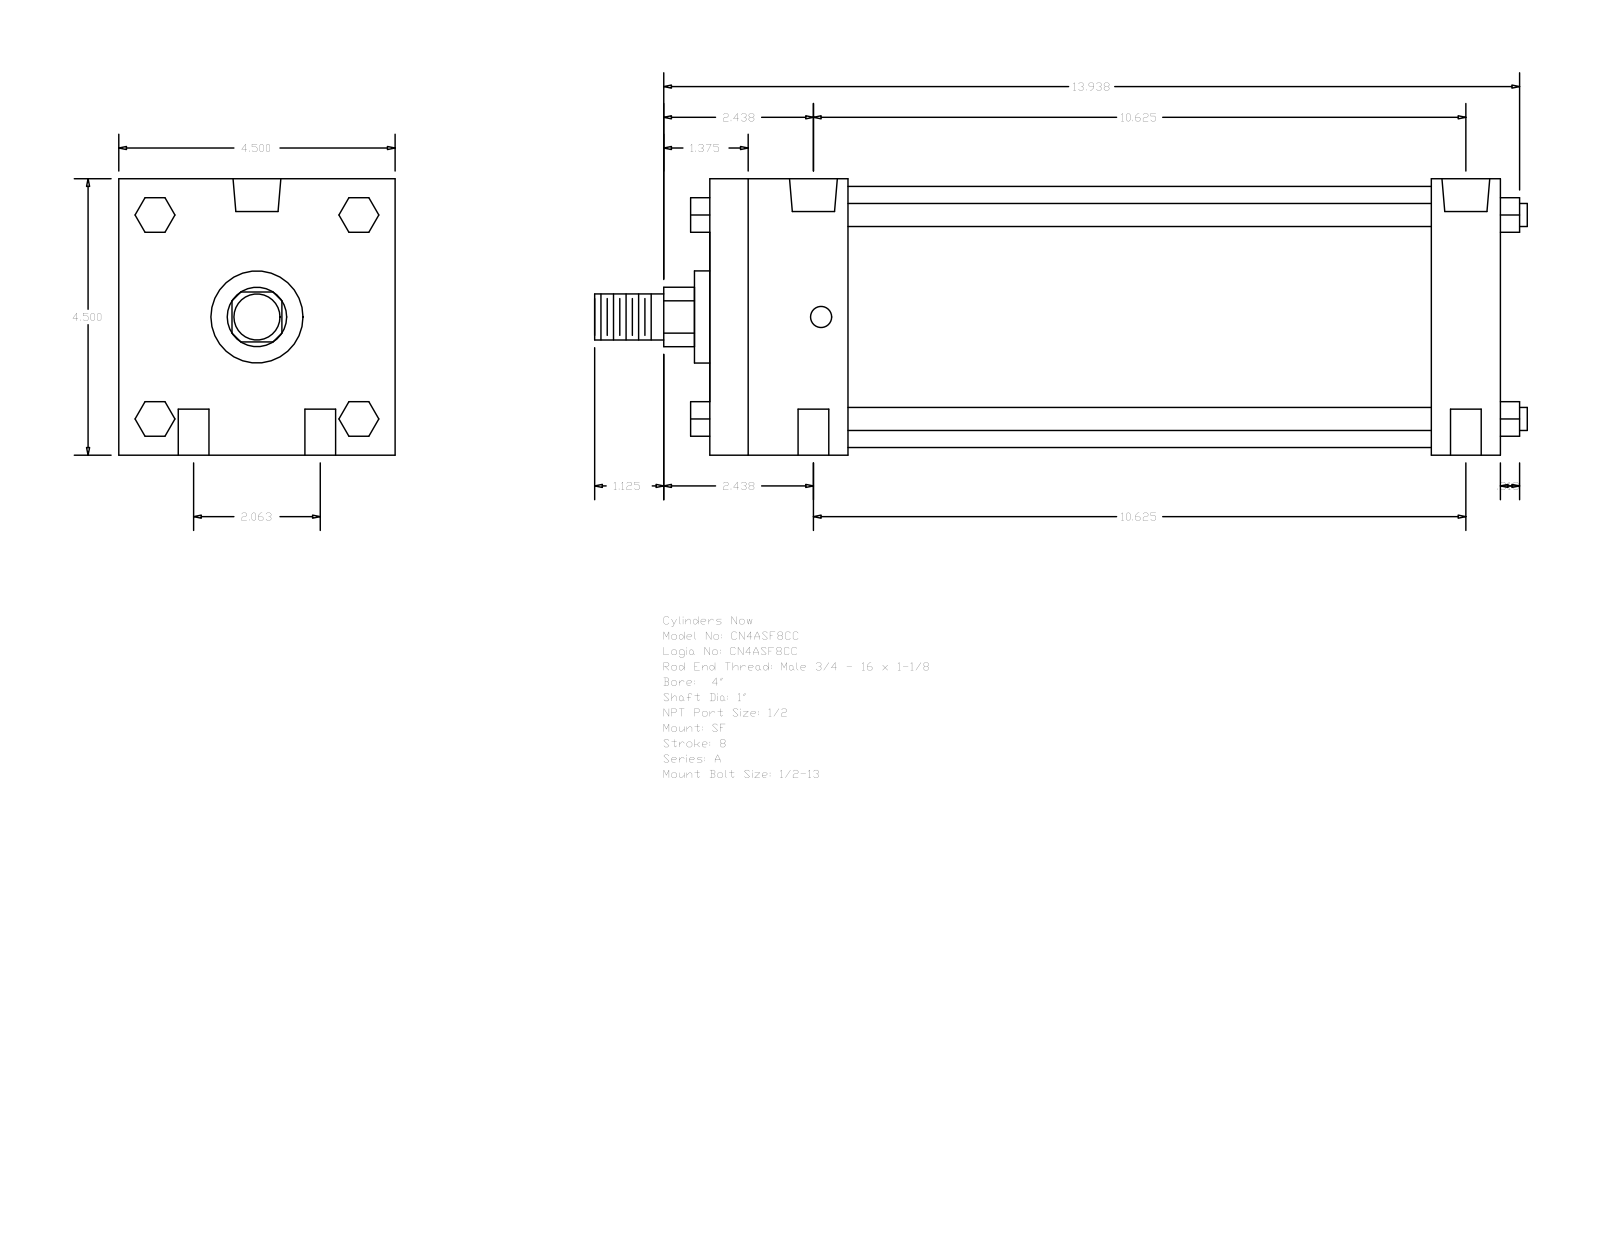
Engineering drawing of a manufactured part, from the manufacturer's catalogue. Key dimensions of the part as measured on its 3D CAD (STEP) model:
Part name (STEP PRODUCT): A_SF__0400_1
STEP written by: GSSL Pune (CONFIG_CONTROL_DESIGN)
Units: millimetres
Bodies: 0 solids, 124 faces (94 planar, 30 cylindrical, 0 other)
Overall size (bounding box): 385.76 × 114.3 × 114.3
Round holes (diameter × count): ⌀12.7 ×4, ⌀8.73 ×2, ⌀19.77 ×2
Round bosses / shafts (diameter × count): ⌀9.53 ×4, ⌀107.95 ×1, ⌀38.1 ×1, ⌀25.4 ×1, ⌀19.05 ×1
Partial cylindrical surfaces — rounded edges, fillets, slot ends (radius × count): R12.29 ×1
Main face-to-face distances: 114.3, 327.02, 28.57, 298.45, 57.15, 241.3, 269.87, 14.29, 42.16, 73.03
Hole centre spacings: 26.19, 271.15, 269.88, 52.38, 274.92, 263.52
